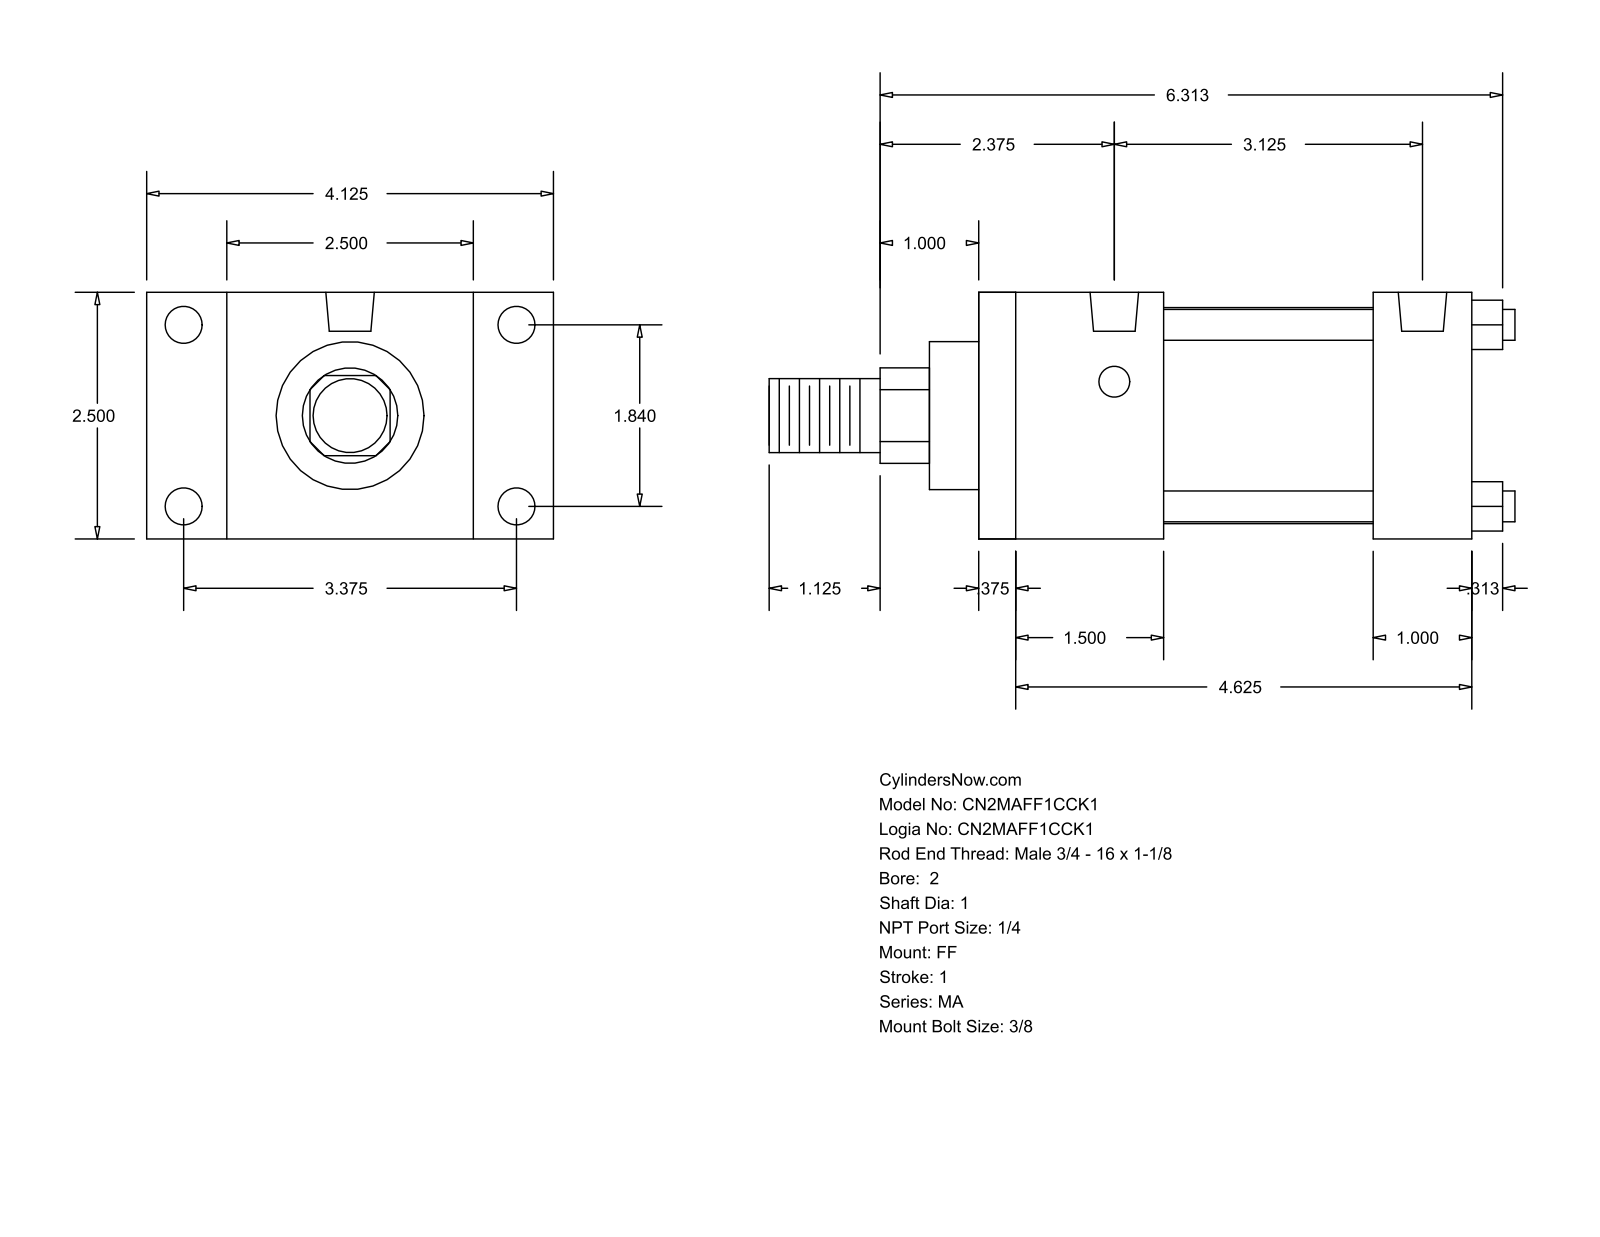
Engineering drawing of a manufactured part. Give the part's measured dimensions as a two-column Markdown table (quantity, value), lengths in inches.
| quantity | value |
| --- | --- |
| part name | MA_FF__0200_1 |
| STEP written by | GSSL Pune (CONFIG_CONTROL_DESIGN) |
| units | inches |
| bodies | 0 solids, 92 faces (64 planar, 28 cylindrical, 0 other) |
| overall size | 7.563 × 4.125 × 2.5 |
| round holes (diameter × count) | 0.313 × 4, 0.375 × 4, 0.492 × 2 |
| round bosses / shafts (diameter × count) | 0.313 × 4, 2.19 × 1, 1.5 × 1, 1 × 1, 0.75 × 1 |
| partial cylindrical surfaces (radius × count) | 0.484 × 1 |
| main face-to-face distances | 2.5, 5, 0.375, 4.625, 2.125, 4, 1, 0.813, 0.5, 1.875 |
| hole center spacings | 1.84, 3.125, 3.375, 3.844 |
